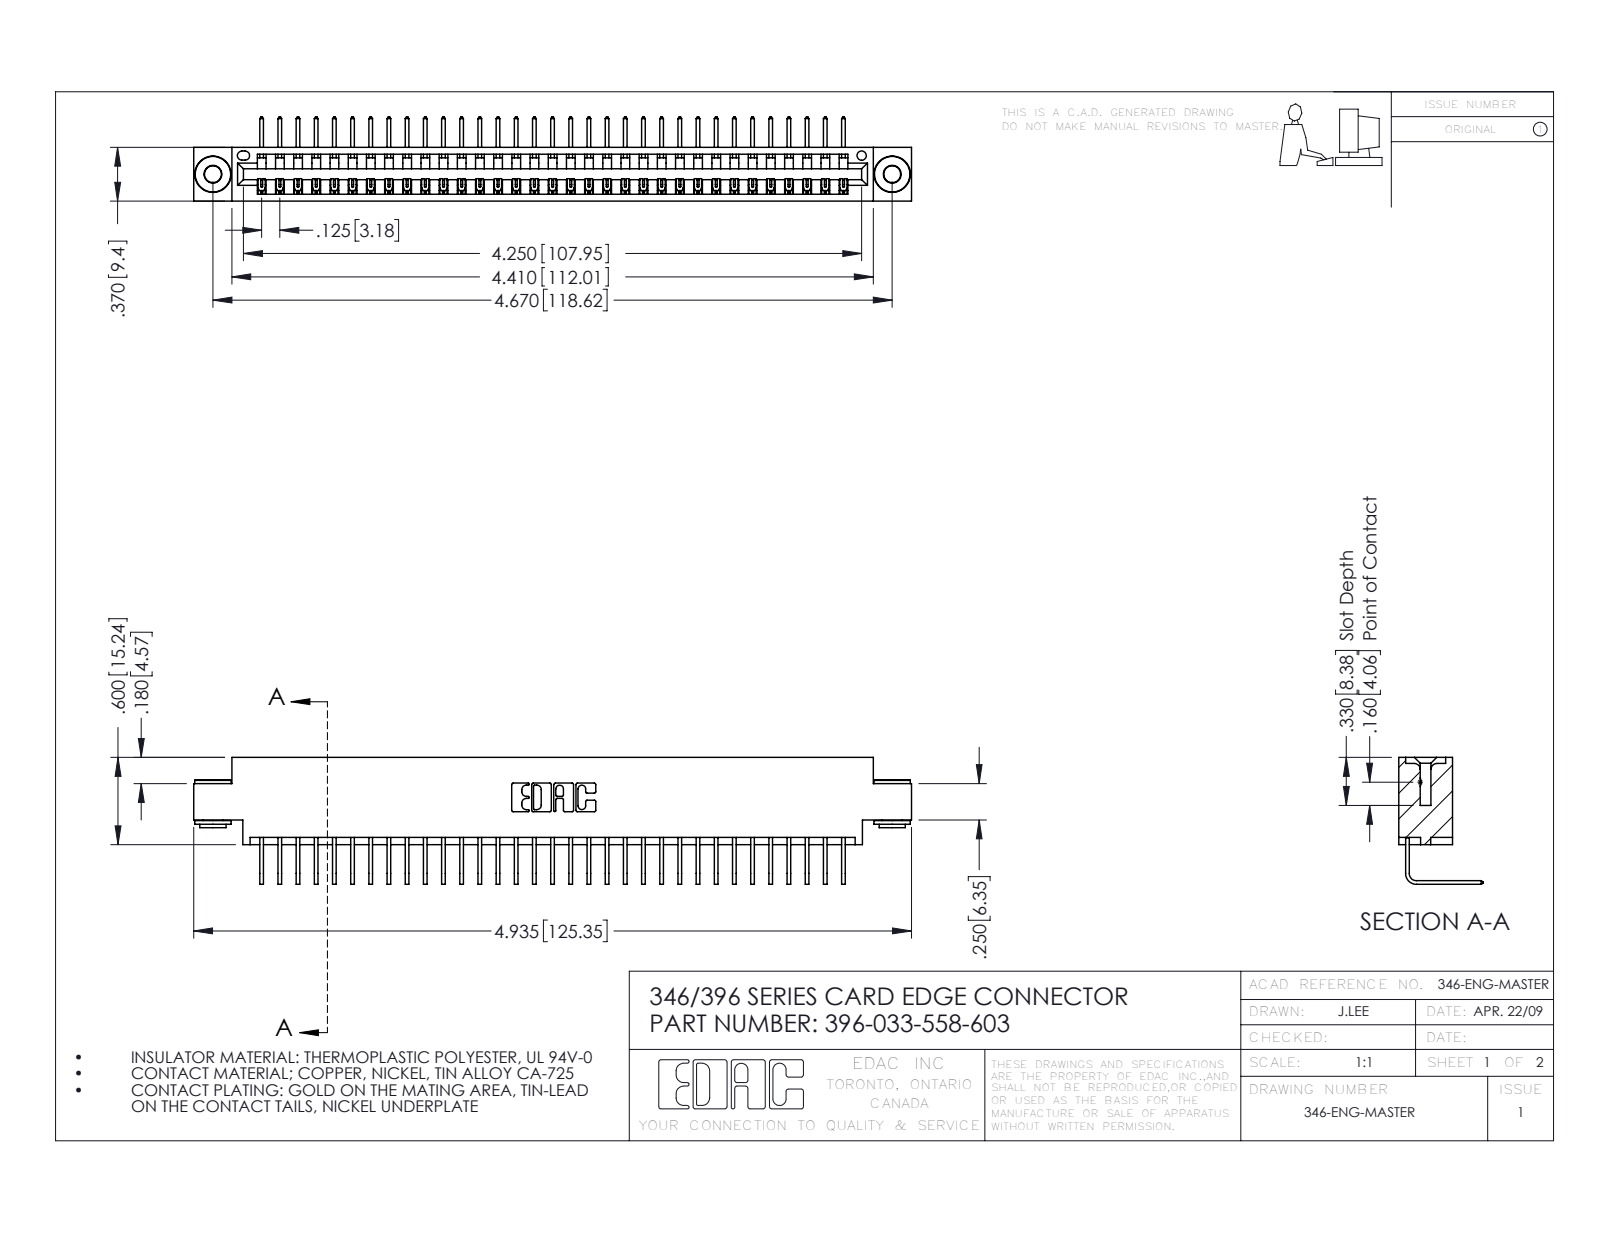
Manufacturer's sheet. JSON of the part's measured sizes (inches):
{"part_name": "396-033-558-603; 345-250-002_345-250-002-102; 346 Part_0.170 Offset - 0.156 Dia-TH; 345-292-001_558 Tail - 2", "step_written_by": "SolidWorks 2016 (CONFIG_CONTROL_DESIGN)", "units": "inches", "bodies": {"solids": 36, "faces": 2144, "planar": 1476, "cylindrical": 660, "other": 8}, "overall_size": [4.935, 0.873, 0.58], "volume_in3": 0.727, "surface_area_in2": 24.53, "round_holes": [[0.116, 2], [0.156, 2], [0.064, 1]], "round_bosses_or_shafts": [[0.25, 2], [0.18, 2], [0.136, 2]], "partial_cylinders_radius": [[0.006, 66], [0.01, 22], [0.007, 6], [0.031, 6], [0.026, 3], [0.031, 2], [0.04, 2], [0.014, 1]], "face_to_face_distances": [0.322, 0.048, 0.37, 0.25, 0.025, 0.298, 0.072, 0.148, 0.222, 0.1], "hole_center_spacings": [0.246, 4.462, 4.67]}
